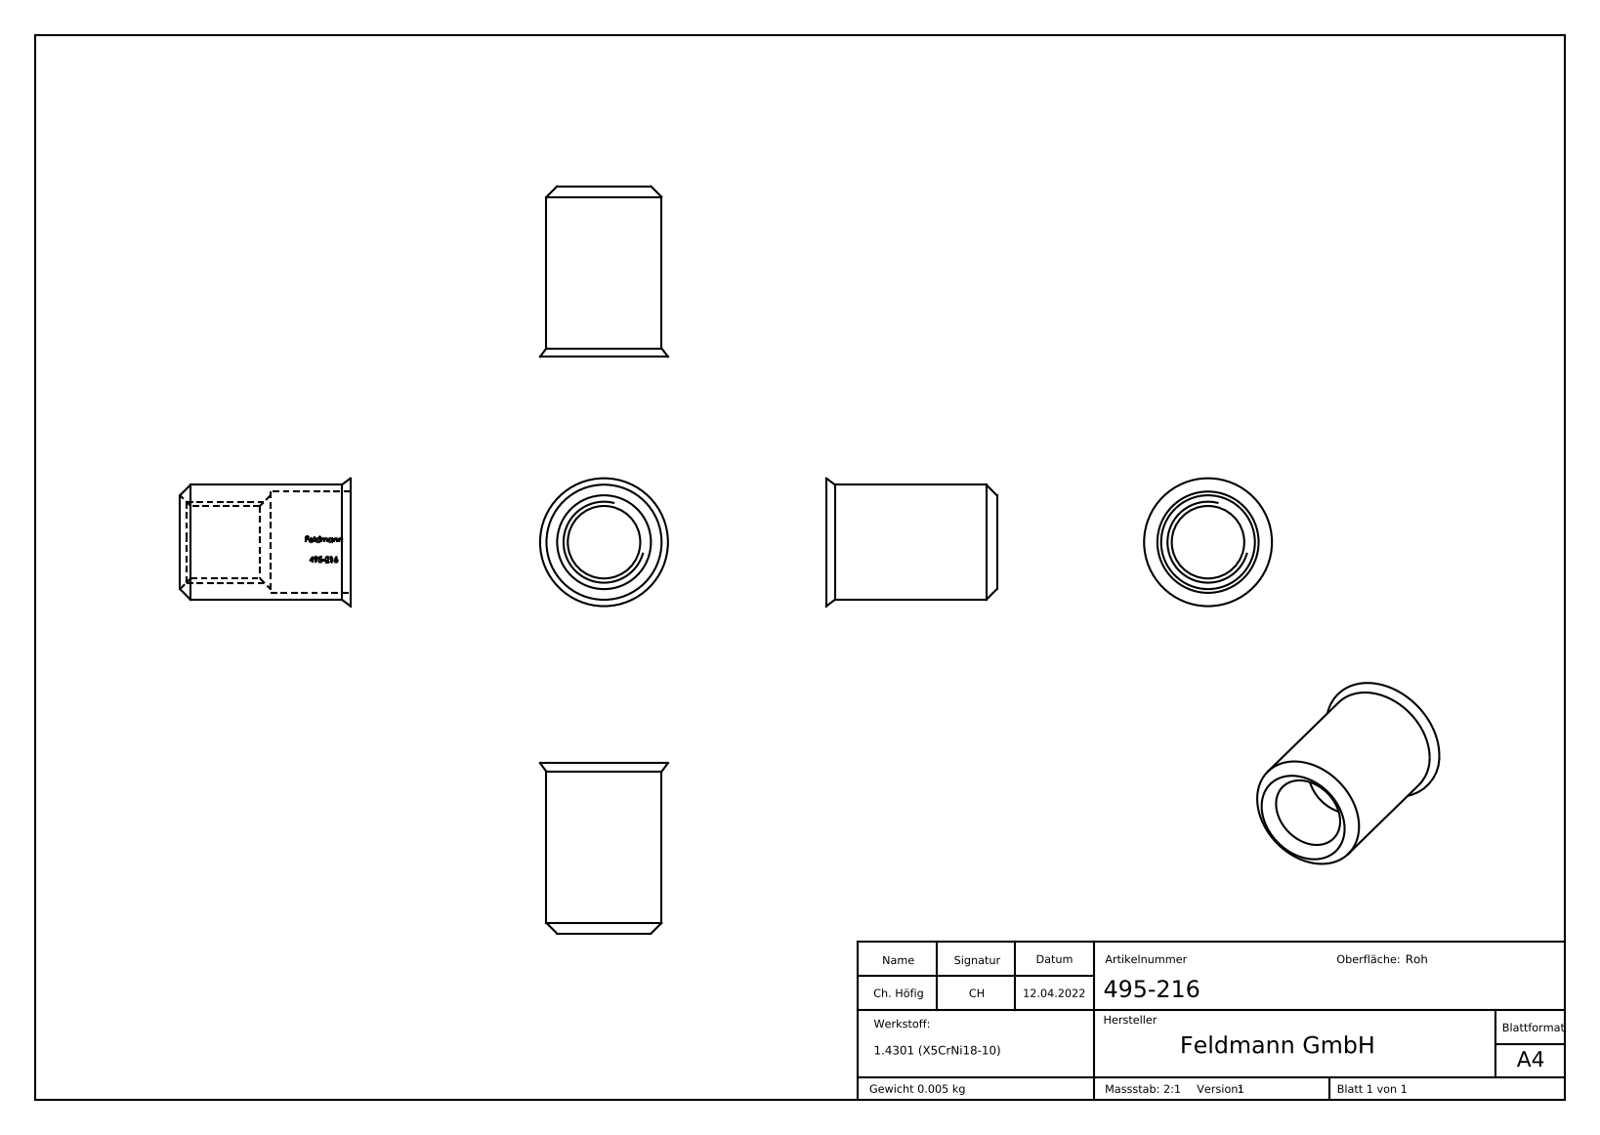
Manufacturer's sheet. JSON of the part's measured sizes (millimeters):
{"part_name": "495-216", "step_written_by": "SolidWorks 2018 (CONFIG_CONTROL_DESIGN)", "units": "millimeters", "bodies": {"solids": 1, "faces": 210, "planar": 100, "cylindrical": 29, "other": 81}, "overall_size": [16, 12, 12], "volume_mm3": 594, "surface_area_mm2": 1049, "round_holes": [[6.8, 1], [9.5, 1]], "round_bosses_or_shafts": [[10.8, 1]], "partial_cylinders_radius": [[4.85, 1]], "face_to_face_distances": [7.5, 1.83, 0.66, 1.35, 1.88, 1.19, 1.67, 1.74, 1.62, 1.79]}
